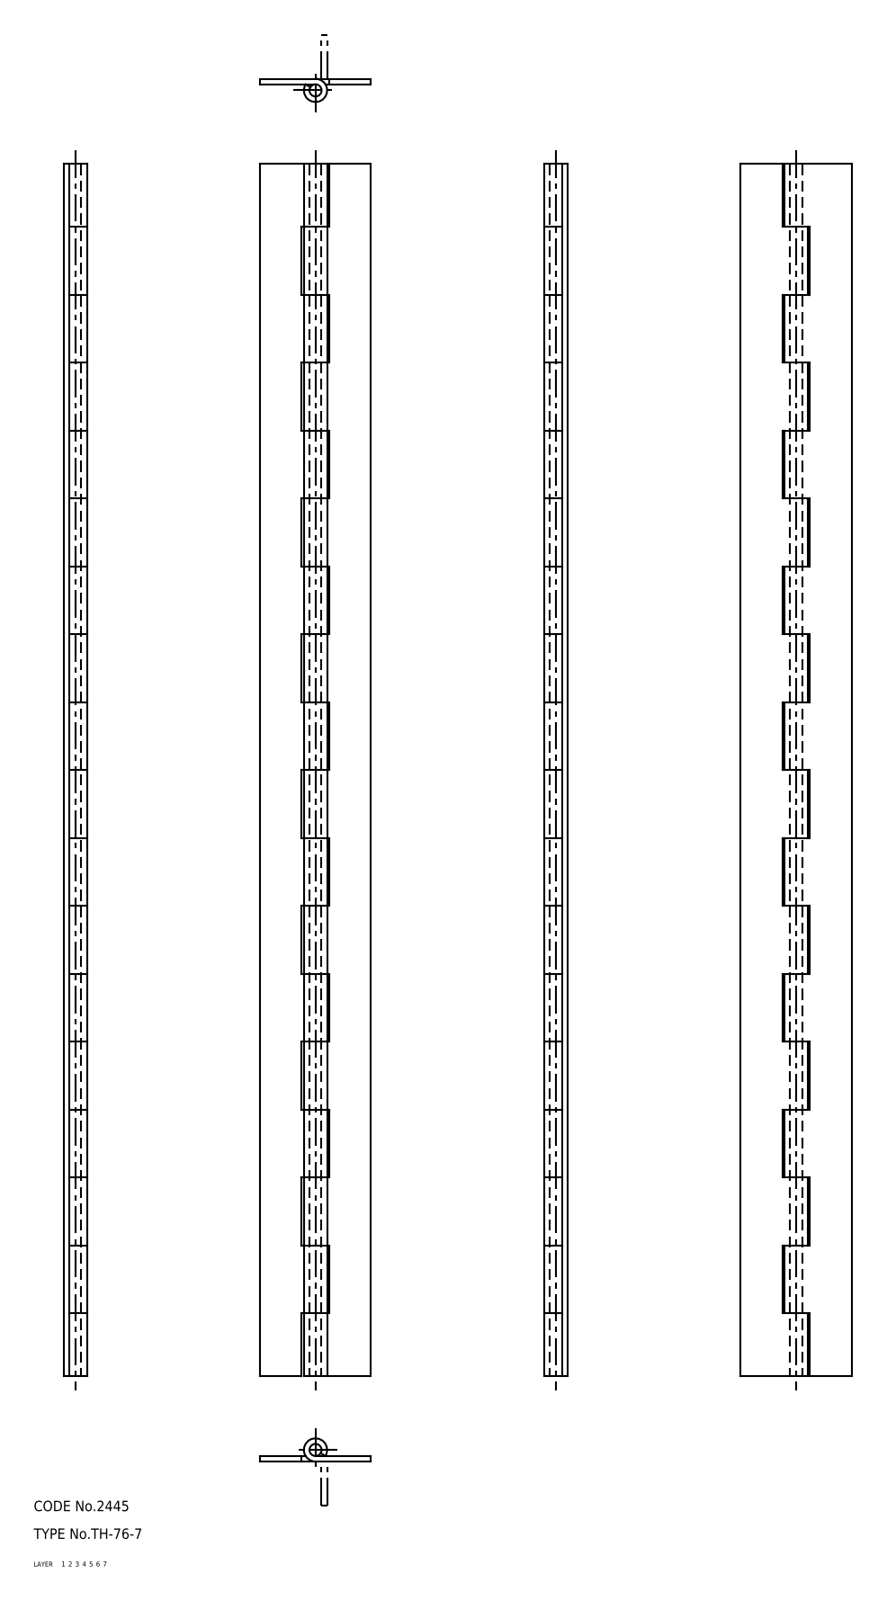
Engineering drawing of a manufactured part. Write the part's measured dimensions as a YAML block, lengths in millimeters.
part_name: "TH_76_7; hinge piece_A; shaft; hinge piece_B"
step_written_by: "SolidWorks 2015 (AUTOMOTIVE_DESIGN)"
units: millimeters
bodies: {solids: 3, faces: 120, planar: 82, cylindrical: 38, other: 0}
overall_size: [350, 32, 6.7]
volume: 26512
surface_area: 36114
round_holes:
  - {diameter: 3.5, count: 1}
round_bosses_or_shafts:
  - {diameter: 6.7, count: 1}
face_to_face_distances: [1.6, 19.6, 39.2, 58.8, 78.4, 98, 117.6, 32, 12, 20]
